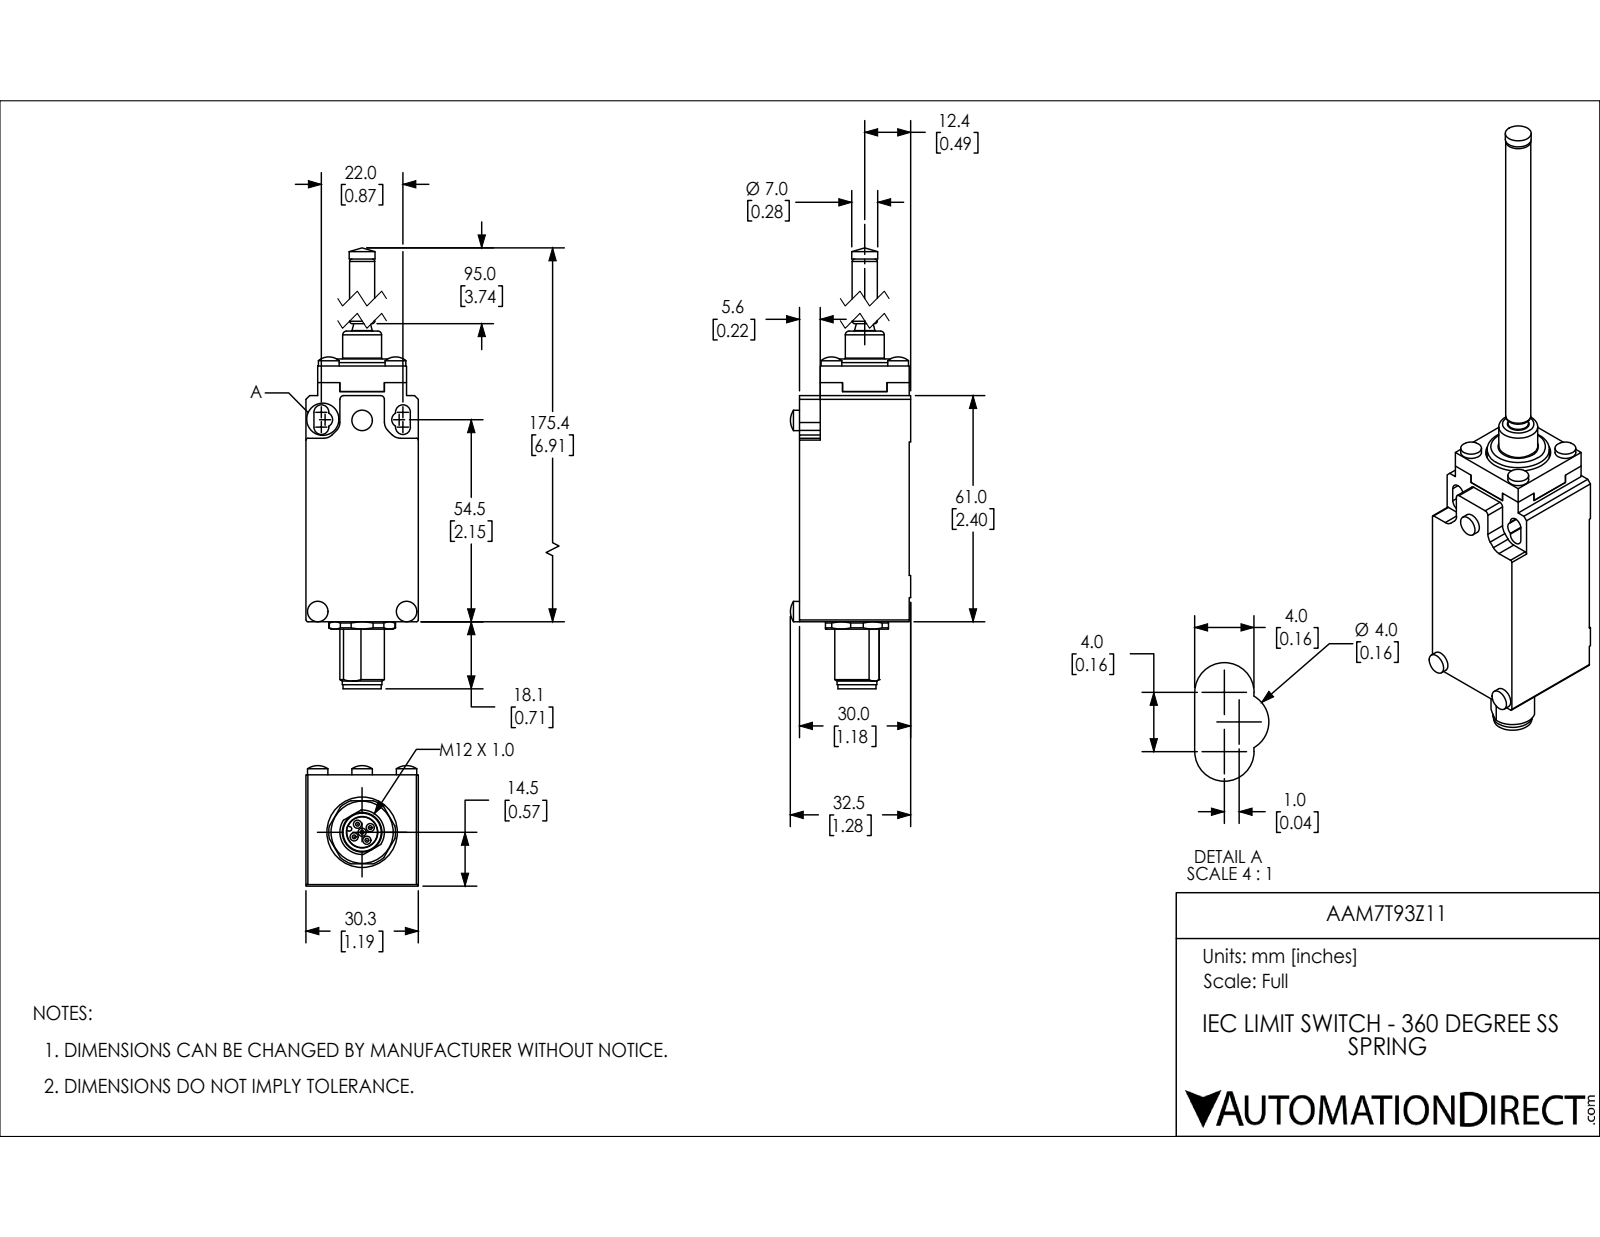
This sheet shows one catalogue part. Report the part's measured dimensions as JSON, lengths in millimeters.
{"part_name": "AAM7T93Z11", "step_written_by": "SolidWorks 2018 (AUTOMOTIVE_DESIGN)", "units": "millimeters", "bodies": {"solids": 4, "faces": 270, "planar": 104, "cylindrical": 111, "other": 55}, "overall_size": [193.5, 32.5, 30.3], "volume_mm3": 63960, "surface_area_mm2": 17660, "round_holes": [[2.2, 5], [13, 1], [14, 1], [16, 1], [17.5, 1]], "round_bosses_or_shafts": [[1.4, 5], [1, 5], [5.6, 4], [5.5, 3], [16.8, 1], [10.7, 1], [10.5, 1], [10.3, 1]], "partial_cylinders_radius": [[2, 6], [0.5, 4], [3, 4], [1, 2], [0.6, 1], [6, 1], [9, 1], [10, 1]], "face_to_face_distances": [30.3, 29.6, 24, 0.4, 30, 62.1, 62.1, 3.1, 27.2, 6], "hole_center_spacings": [2.5, 3.5, 5, 1.2, 2.1, 2.4, 3.9, 4.5]}
